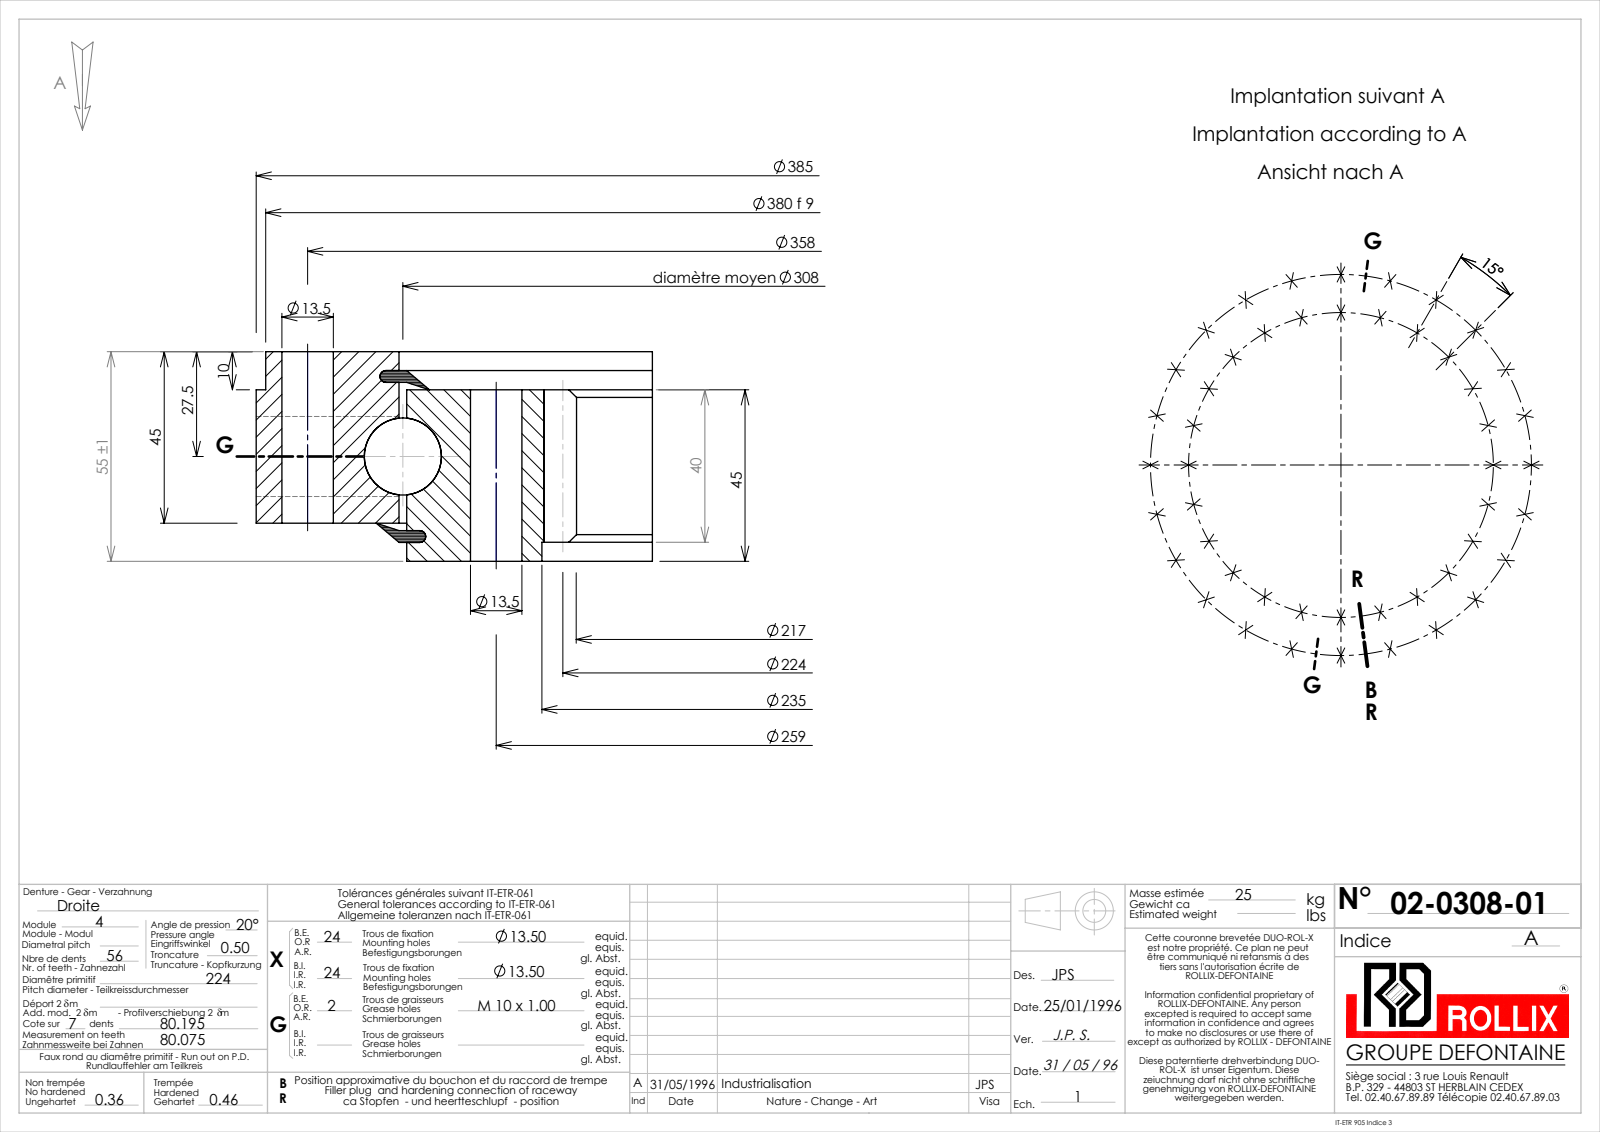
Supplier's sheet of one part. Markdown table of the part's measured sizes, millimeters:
| quantity | value |
| --- | --- |
| part name | 02-0308-01 |
| STEP written by | SolidWorks 2016 (CONFIG_CONTROL_DESIGN) |
| units | millimeters |
| bodies | 5 solids, 497 faces (126 planar, 231 cylindrical, 140 other) |
| overall size | 385 × 385 × 55 |
| volume | 2 764 000 mm³ |
| surface area | 521 735 mm² |
| round holes (diameter × count) | 13.5 × 48, 9 × 2, 235 × 1, 310.02 × 1 |
| round bosses / shafts (diameter × count) | 385 × 1, 380 × 1, 305.98 × 1 |
| partial cylindrical surfaces (radius × count) | 108.5 × 1, 117 × 1 |
| main face-to-face distances | 45, 10, 35, 55, 8.05, 46.95, 1.95, 36.95, 4.95, 50.05 |
| hole center spacings | 129.5, 157.67, 205.48, 67.03, 224.3, 33.81, 99.11, 183.14 |
